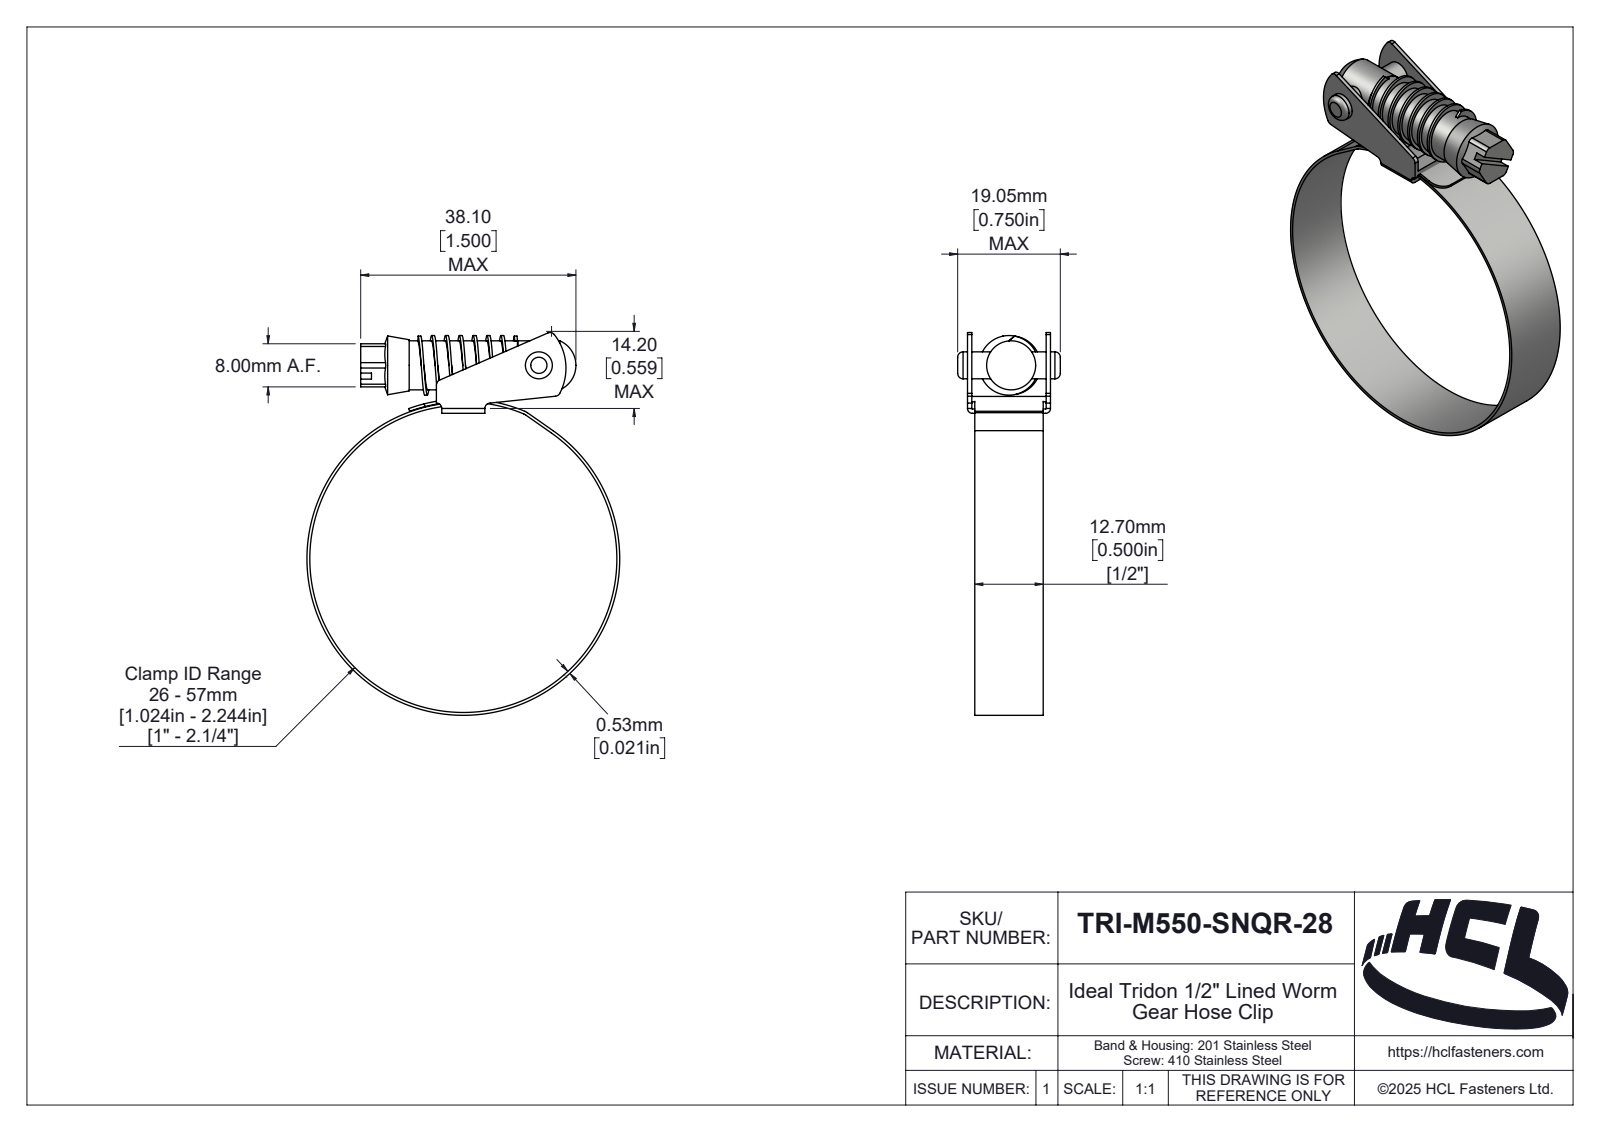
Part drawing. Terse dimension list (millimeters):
name: TRI-M550-SNQR-28
written by: SolidWorks 2025 (AUTOMOTIVE_DESIGN)
unit: mm
bodies: 5 solids, 222 faces (44 planar, 112 cylindrical, 66 other)
size: 71.02 × 58.06 × 19.05
volume: 4 466 mm³; area: 8 645 mm²
holes: 1× ⌀5, 1× ⌀57
bosses: 1× ⌀58.06, 1× ⌀9.1
rounds: 11× R1, 2× R0.1, 2× R0.9, 2× R3, 1× R0.46, 1× R1.89, 1× R2, 1× R2.35
face distances: 0.8, 14.6, 1.35, 14.05, 0.55, 13.25, 15.4, 13.8, 1, 12.7
hole spacings: 38.54
